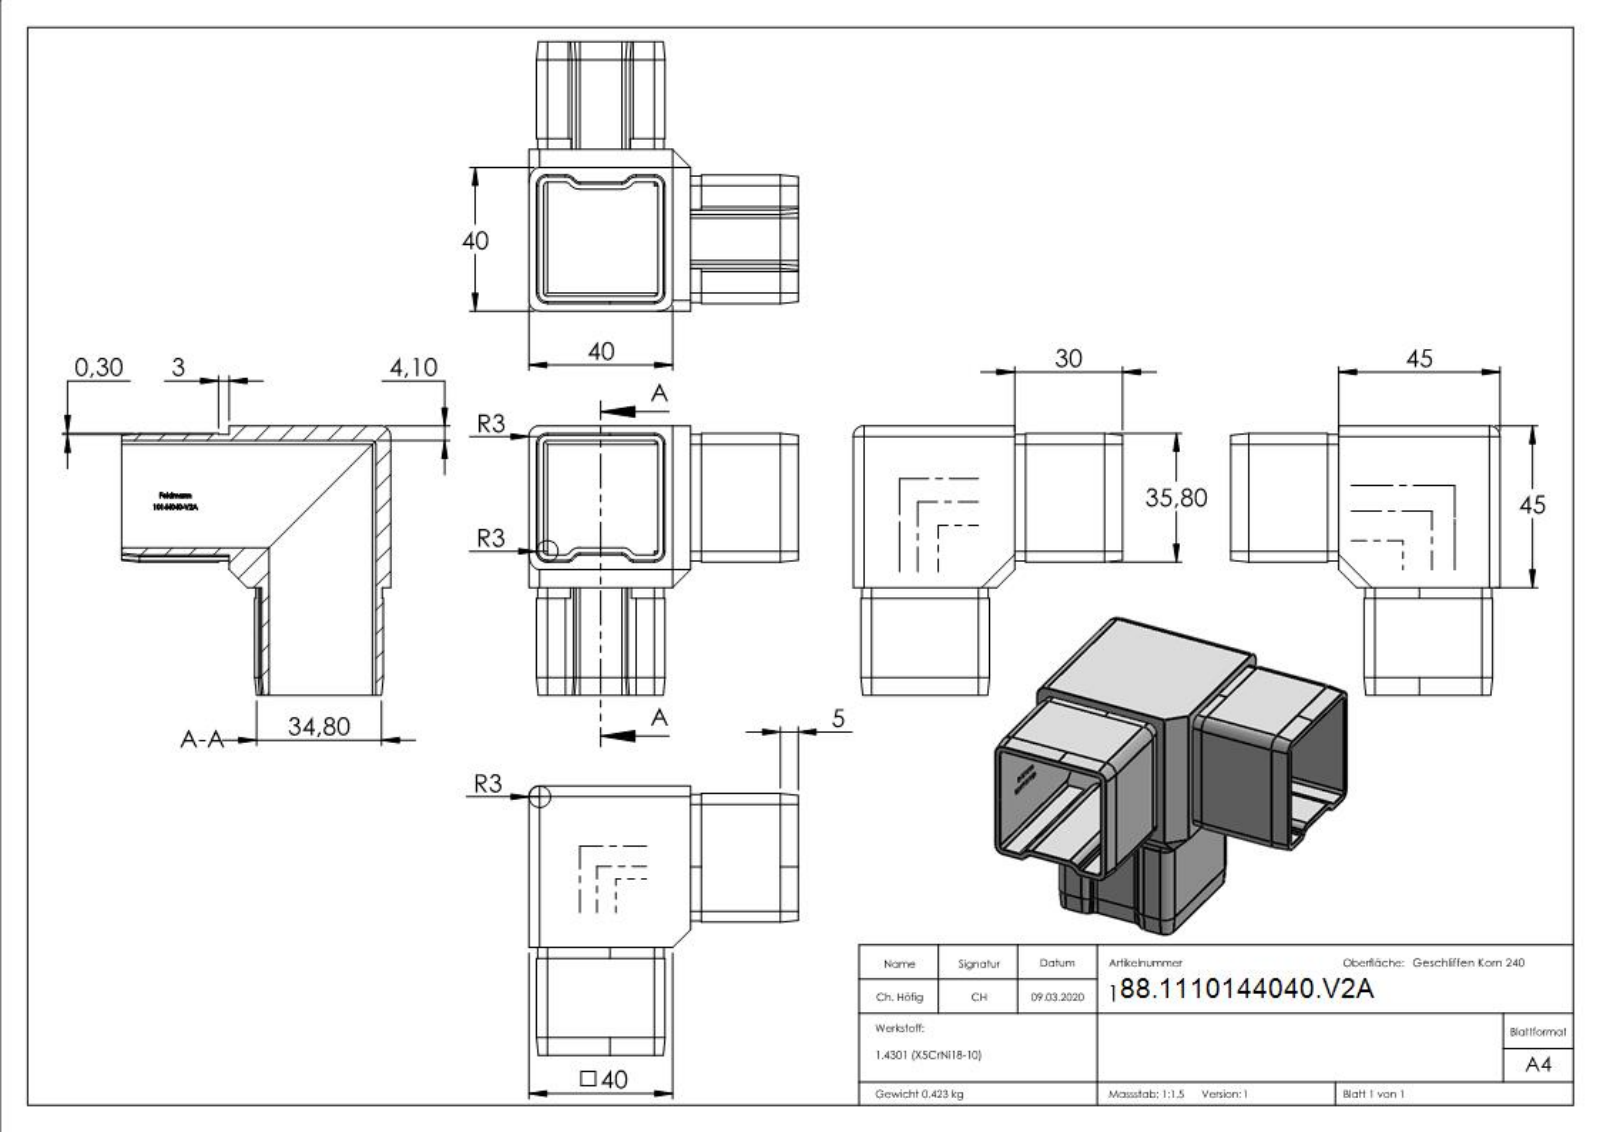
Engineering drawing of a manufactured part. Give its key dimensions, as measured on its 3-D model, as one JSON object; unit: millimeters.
{"part_name": "10144040-V2A", "step_written_by": "SolidWorks 2015 (CONFIG_CONTROL_DESIGN)", "units": "millimeters", "bodies": {"solids": 1, "faces": 469, "planar": 297, "cylindrical": 66, "other": 106}, "overall_size": [75, 75, 75], "volume_mm3": 53594, "surface_area_mm2": 39063, "partial_cylinders_radius": [[3, 17], [1, 12], [2.7, 12], [1.27, 10], [1.5, 6], [3.5, 6], [3.27, 2]], "face_to_face_distances": [2, 31.8, 33.8, 4.1, 35.9, 2.1, 37.9, 35.8, 33.9, 29.8]}
